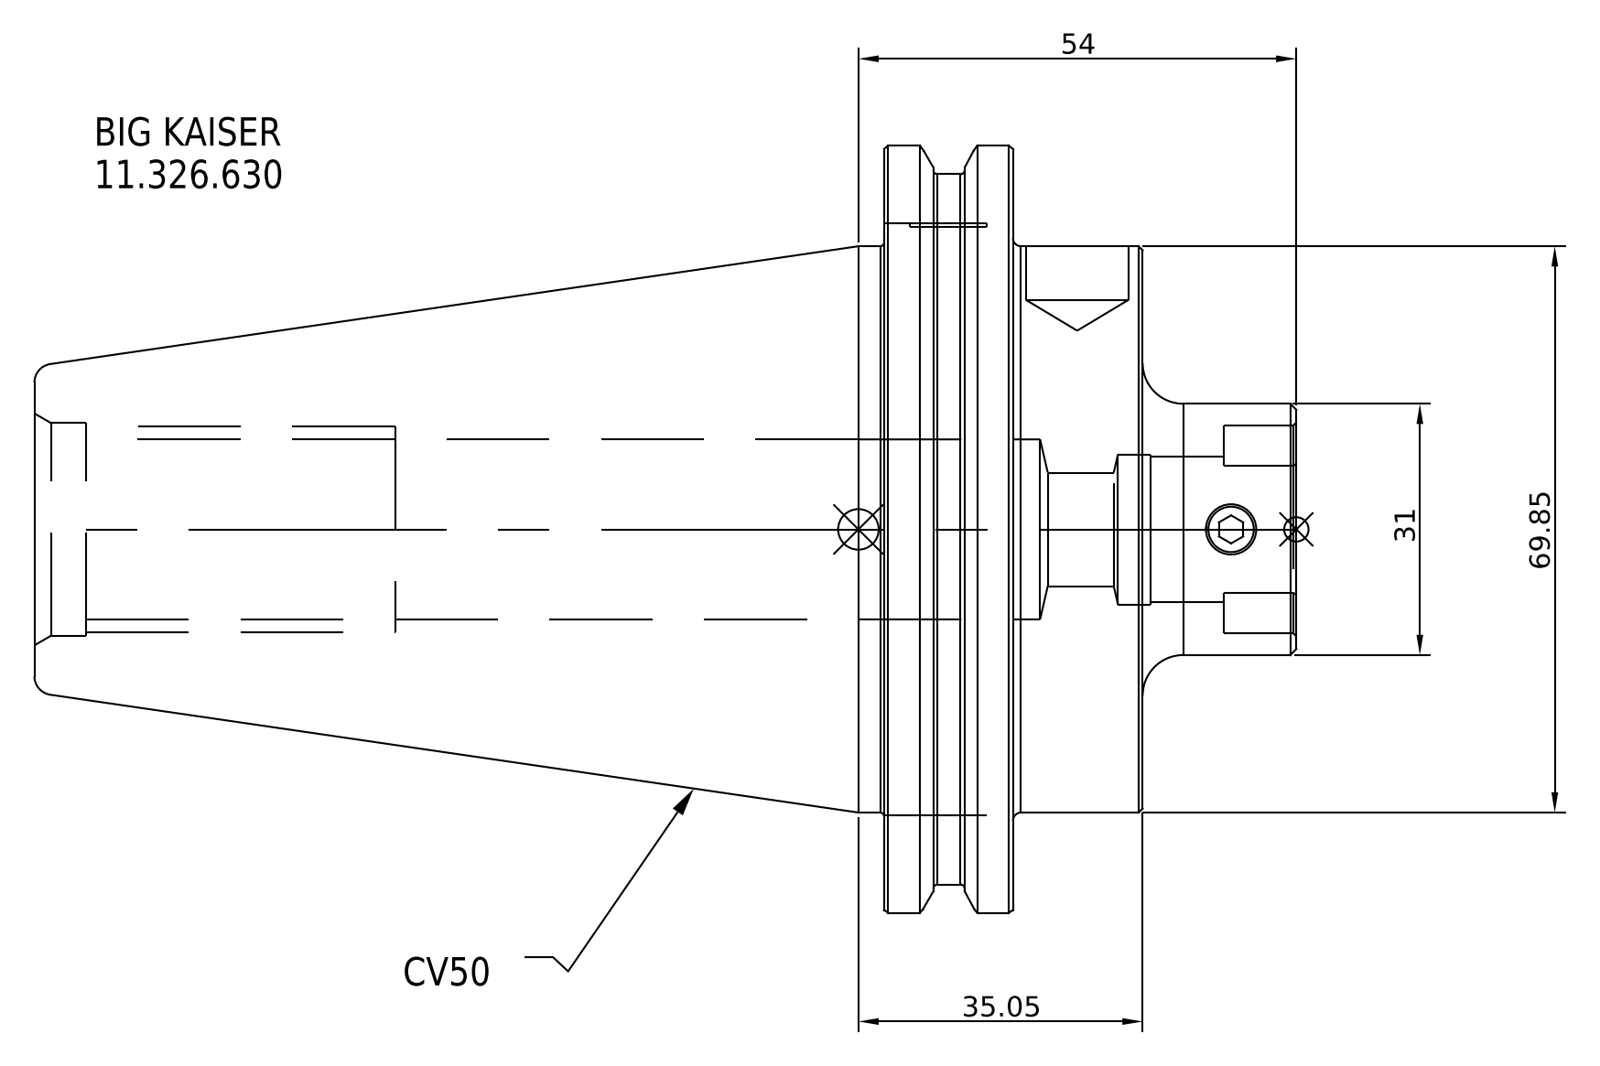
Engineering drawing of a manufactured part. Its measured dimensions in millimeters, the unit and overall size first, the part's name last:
Units: millimetres
Overall size (bounding box): 155.6 × 98.43 × 98.43
Round bosses / shafts (diameter × count): ⌀98.43 ×1, ⌀91.29 ×1, ⌀69.85 ×1, ⌀31 ×1
Main face-to-face distances: 17.55, 15.95, 33.5, 136.6, 120.65, 103.1, 19, 34.95, 52.5, 155.6
Volume: 456 821 mm³ · Surface area: 42 823 mm²
Bodies: 1 solid, 16 faces (7 planar, 6 cylindrical, 3 other)
Part name (STEP PRODUCT): 11.326.630
STEP written by: SolidWorks 2021 (CONFIG_CONTROL_DESIGN)
